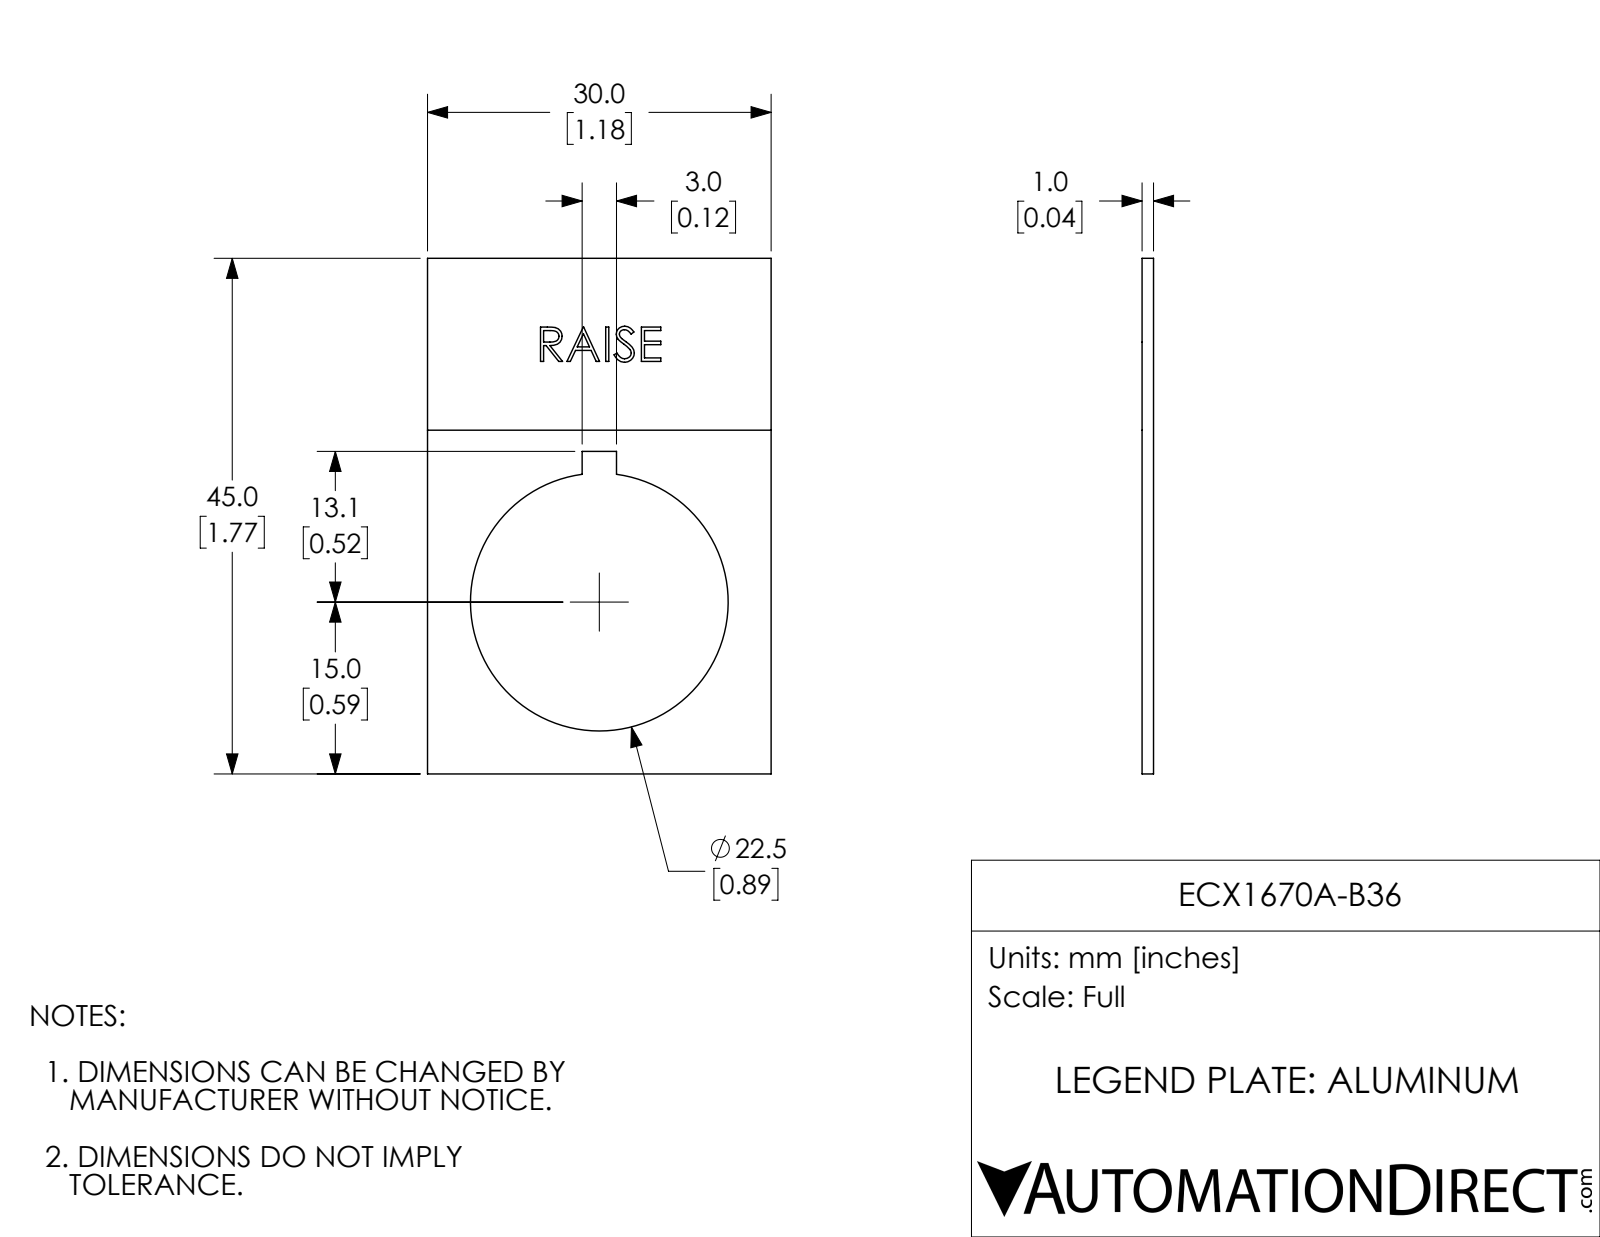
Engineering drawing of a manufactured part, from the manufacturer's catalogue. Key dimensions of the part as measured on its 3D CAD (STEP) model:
Part name (STEP PRODUCT): ECX1670A-B36
STEP written by: SolidWorks 2017 (AUTOMOTIVE_DESIGN)
Units: inches
Bodies: 1 solid, 80 faces (57 planar, 3 cylindrical, 20 other)
Overall size (bounding box): 1.772 × 1.181 × 0.039
Volume: 0.058 in³ · Surface area: 3.285 in²
Round holes (diameter × count): ⌀0.886 ×1
Main face-to-face distances: 0.039, 1.181, 1.772, 0.038, 0.531, 0.65, 1.108, 0.663, 0.118, 0.012
